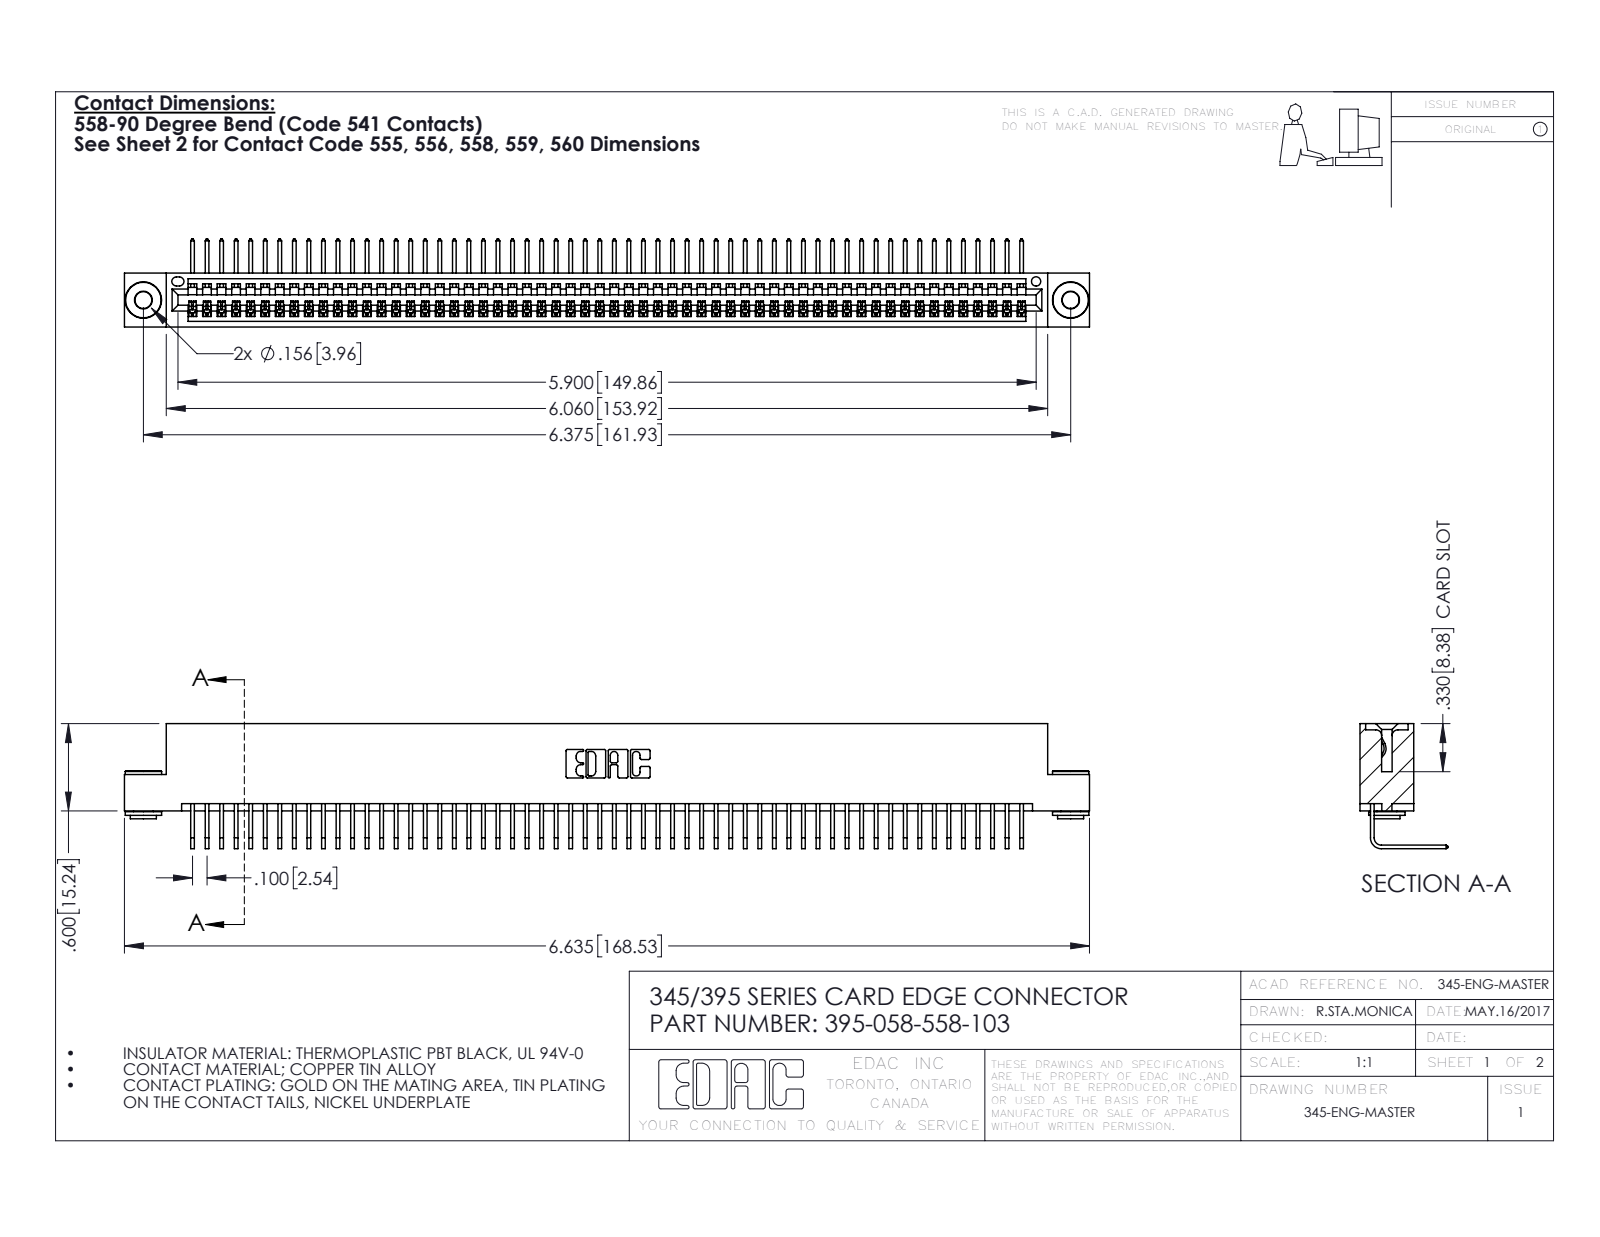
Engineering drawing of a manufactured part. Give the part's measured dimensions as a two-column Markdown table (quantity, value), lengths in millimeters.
| quantity | value |
| --- | --- |
| part name | 345-250-002_345-250-002-102; 395-058-558-103; 345 Part_Flush Mounting Lugs - 0.156 Dia-TH; 345-292-001_558 Tail - 2 |
| STEP written by | SolidWorks 2016 (CONFIG_CONTROL_DESIGN) |
| units | millimeters |
| bodies | 61 solids, 3644 faces (2526 planar, 1110 cylindrical, 8 other) |
| overall size | 168.5 × 21.8 × 15.4 |
| volume | 16 400 mm³ |
| surface area | 23 300 mm² |
| round holes (diameter × count) | 2.9 × 2, 4 × 2, 1.6 × 1 |
| round bosses / shafts (diameter × count) | 6.4 × 2, 4.6 × 2, 3.5 × 2 |
| partial cylindrical surfaces (radius × count) | 0.2 × 116, 0.3 × 22, 0.2 × 6, 0.8 × 6, 0.7 × 3, 0.8 × 2, 1 × 2, 0.4 × 1 |
| main face-to-face distances | 1.8, 7.6, 9.4, 5.1, 0.6, 2.5, 6.9, 5.7, 3.8, 1.8 |
| hole center spacings | 6.9, 155.9, 161.9 |
